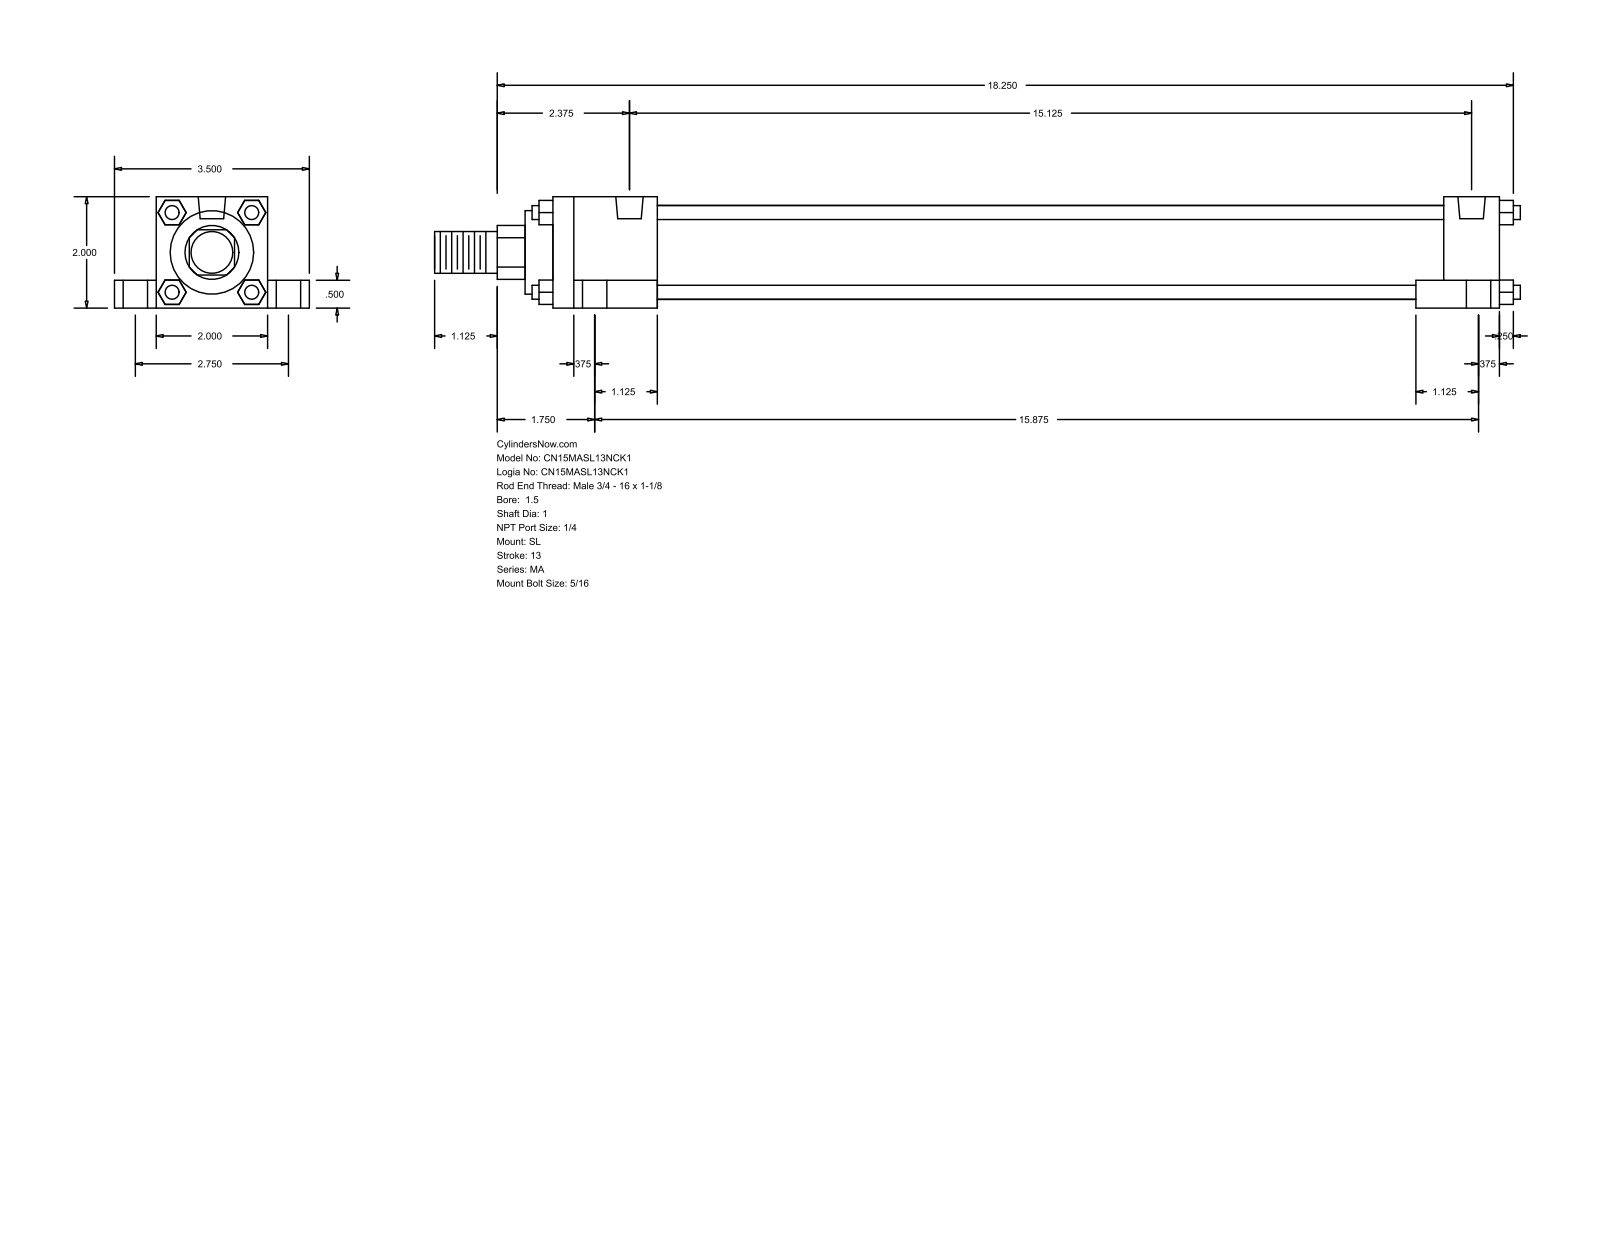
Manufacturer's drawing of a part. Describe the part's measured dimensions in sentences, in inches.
The part is named "MA_SL__0150_1". Its 3-D file was written by "GSSL Pune (CONFIG_CONTROL_DESIGN)". It is 0 solids with 148 faces: 112 planar, 36 cylindrical and 0 other. Overall it measures 19.5 by 3.5 by 2 inches. Round holes: 4 of diameter 0.313, 4 of diameter 0.437, 4 of diameter 0.687, 2 of diameter 0.492. Round bosses or shafts: 4 of diameter 0.25, 1 of diameter 1.69, 1 of diameter 1.5, 1 of diameter 1, 1 of diameter 0.75. Partial cylindrical surfaces (rounded edges, fillets, slot ends): 1 of radius 0.484. The main face-to-face distances are 2, 0.5, 0.75, 2.75, 1.5, 0.375, 17, 1, 0.25, 16. The hole center spacings are 1.38, 1.51, 2.75, 15.125, 15.312, 15.81, 15.875, 16.111.
